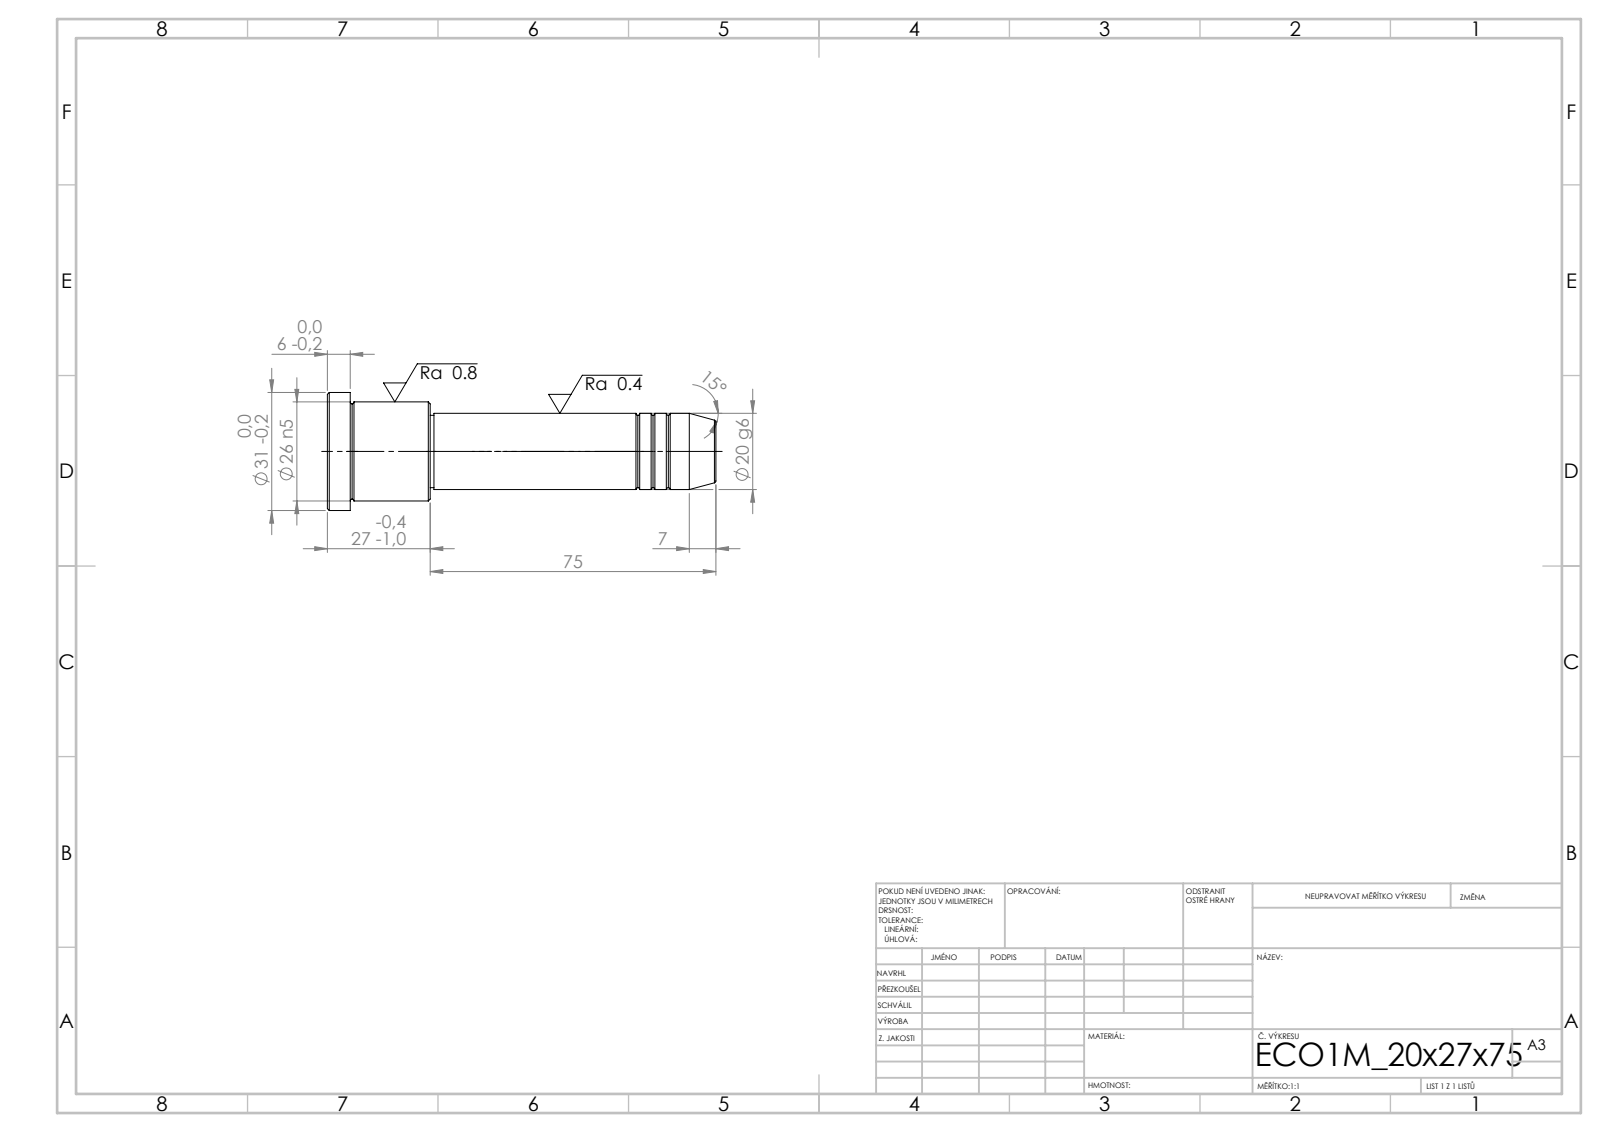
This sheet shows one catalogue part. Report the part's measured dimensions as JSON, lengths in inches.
{"step_written_by": "SolidWorks 2019 (CONFIG_CONTROL_DESIGN)", "units": "inches", "bodies": {"solids": 1, "faces": 43, "planar": 5, "cylindrical": 14, "other": 24}, "overall_size": [4.016, 1.22, 1.22], "volume_in3": 2.361, "surface_area_in2": 13.22, "round_bosses_or_shafts": [[1.22, 1], [1.024, 1], [0.787, 1], [0.748, 1]], "face_to_face_distances": [0.236, 0.827, 1.063, 2.953, 3.78, 4.016, 2.913, 0.039, 0.866, 1.102]}
